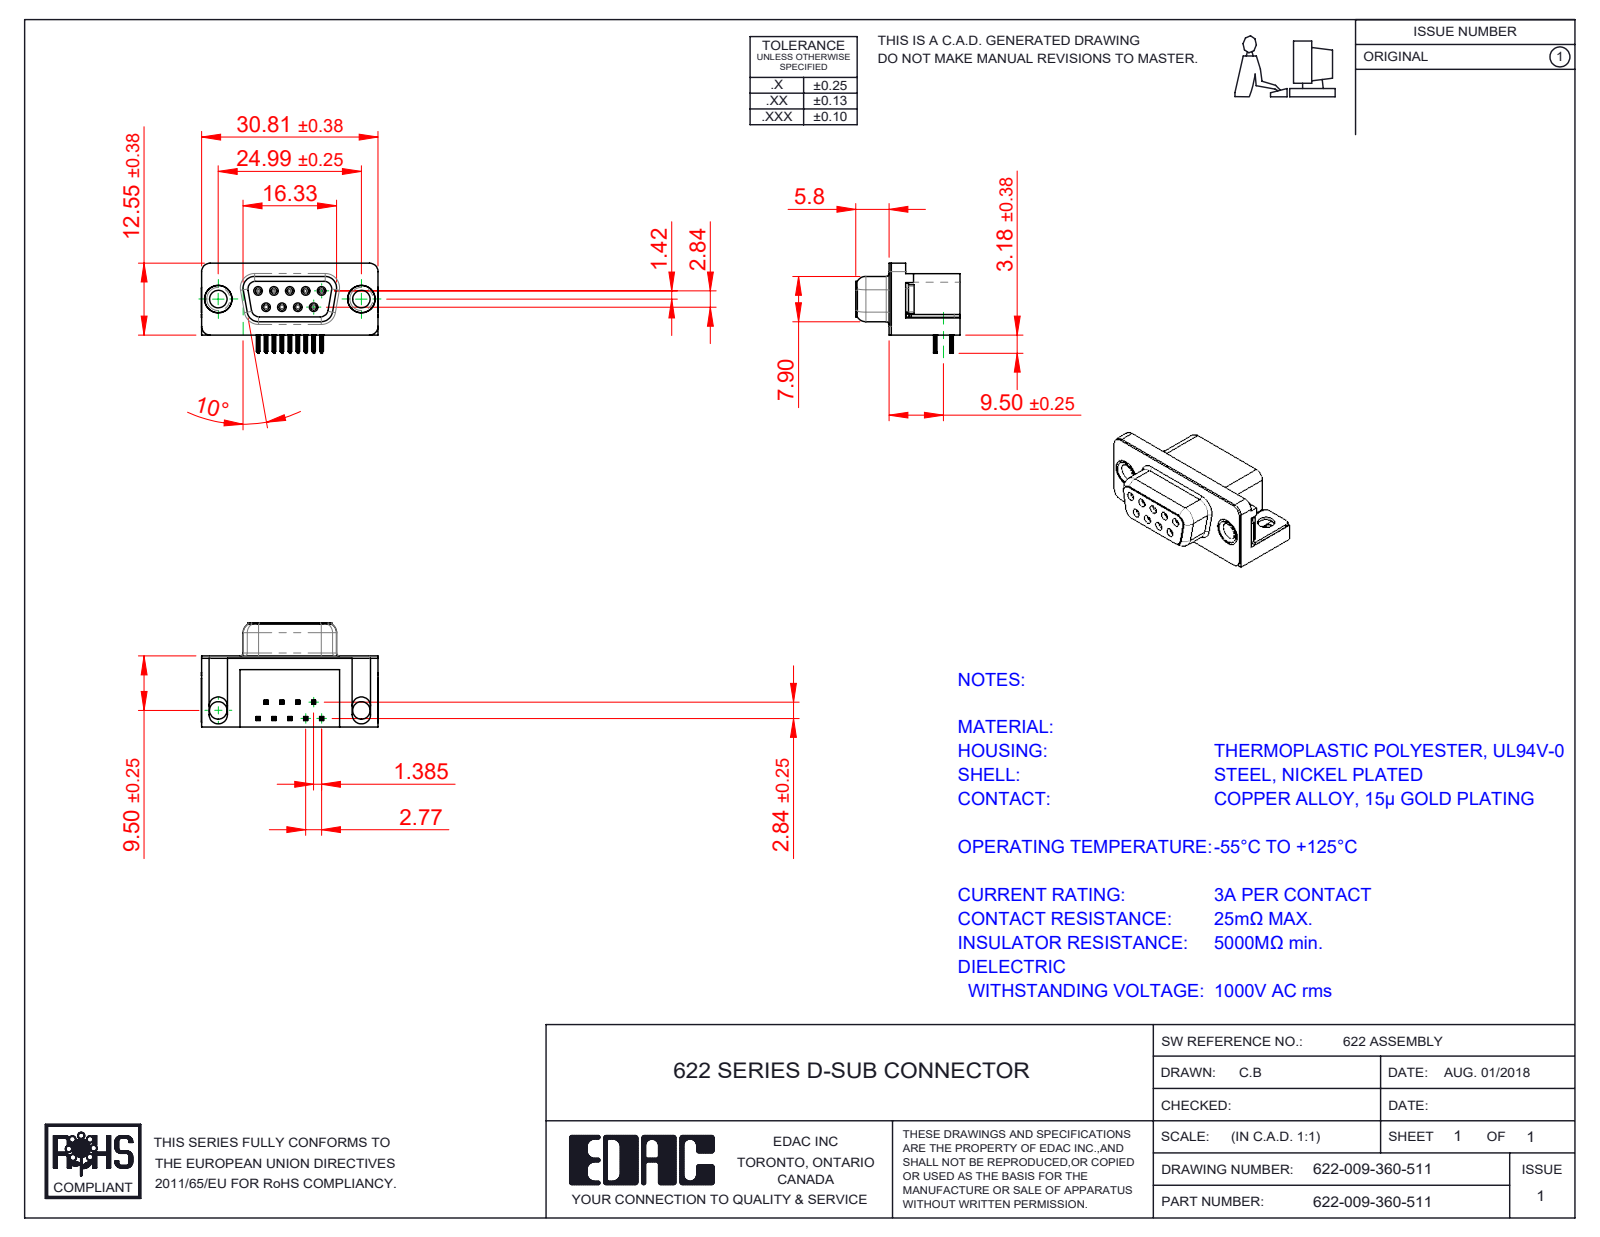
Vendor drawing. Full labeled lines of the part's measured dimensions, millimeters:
Part name (STEP PRODUCT): 622 Shell_9 Socket; 622 Housing_9 Socket; 622 Thru Hole Board Mount; 622 Contact Top (+3 more)
STEP written by: SolidWorks 2016 (CONFIG_CONTROL_DESIGN)
Units: millimetres
Bodies: 15 solids, 1530 faces (682 planar, 398 cylindrical, 450 other)
Overall size (bounding box): 30.89 × 18.2 × 15.73
Volume: 3 711 mm³ · Surface area: 5 037 mm²
Round holes (diameter × count): ⌀0.8 ×9, ⌀0.9 ×9, ⌀3.05 ×4, ⌀4 ×2, ⌀4.8 ×2, ⌀5 ×2
Round bosses / shafts (diameter × count): ⌀1.2 ×9, ⌀4.9 ×2, ⌀4.75 ×2, ⌀3.85 ×2
Partial cylindrical surfaces — rounded edges, fillets, slot ends (radius × count): R0.1 ×72, R0.15 ×36, R0.35 ×18, R1 ×18, R0.34 ×9, R0.25 ×8, R1.35 ×8, R1.6 ×8
Main face-to-face distances: 0.4, 12, 12.4, 0.35, 2.9, 2.5, 6.2, 10.34, 0.5, 9.5
Hole centre spacings: 3.16, 2.77, 5.54, 5.03, 5.04, 8.31, 7.48, 7.49
